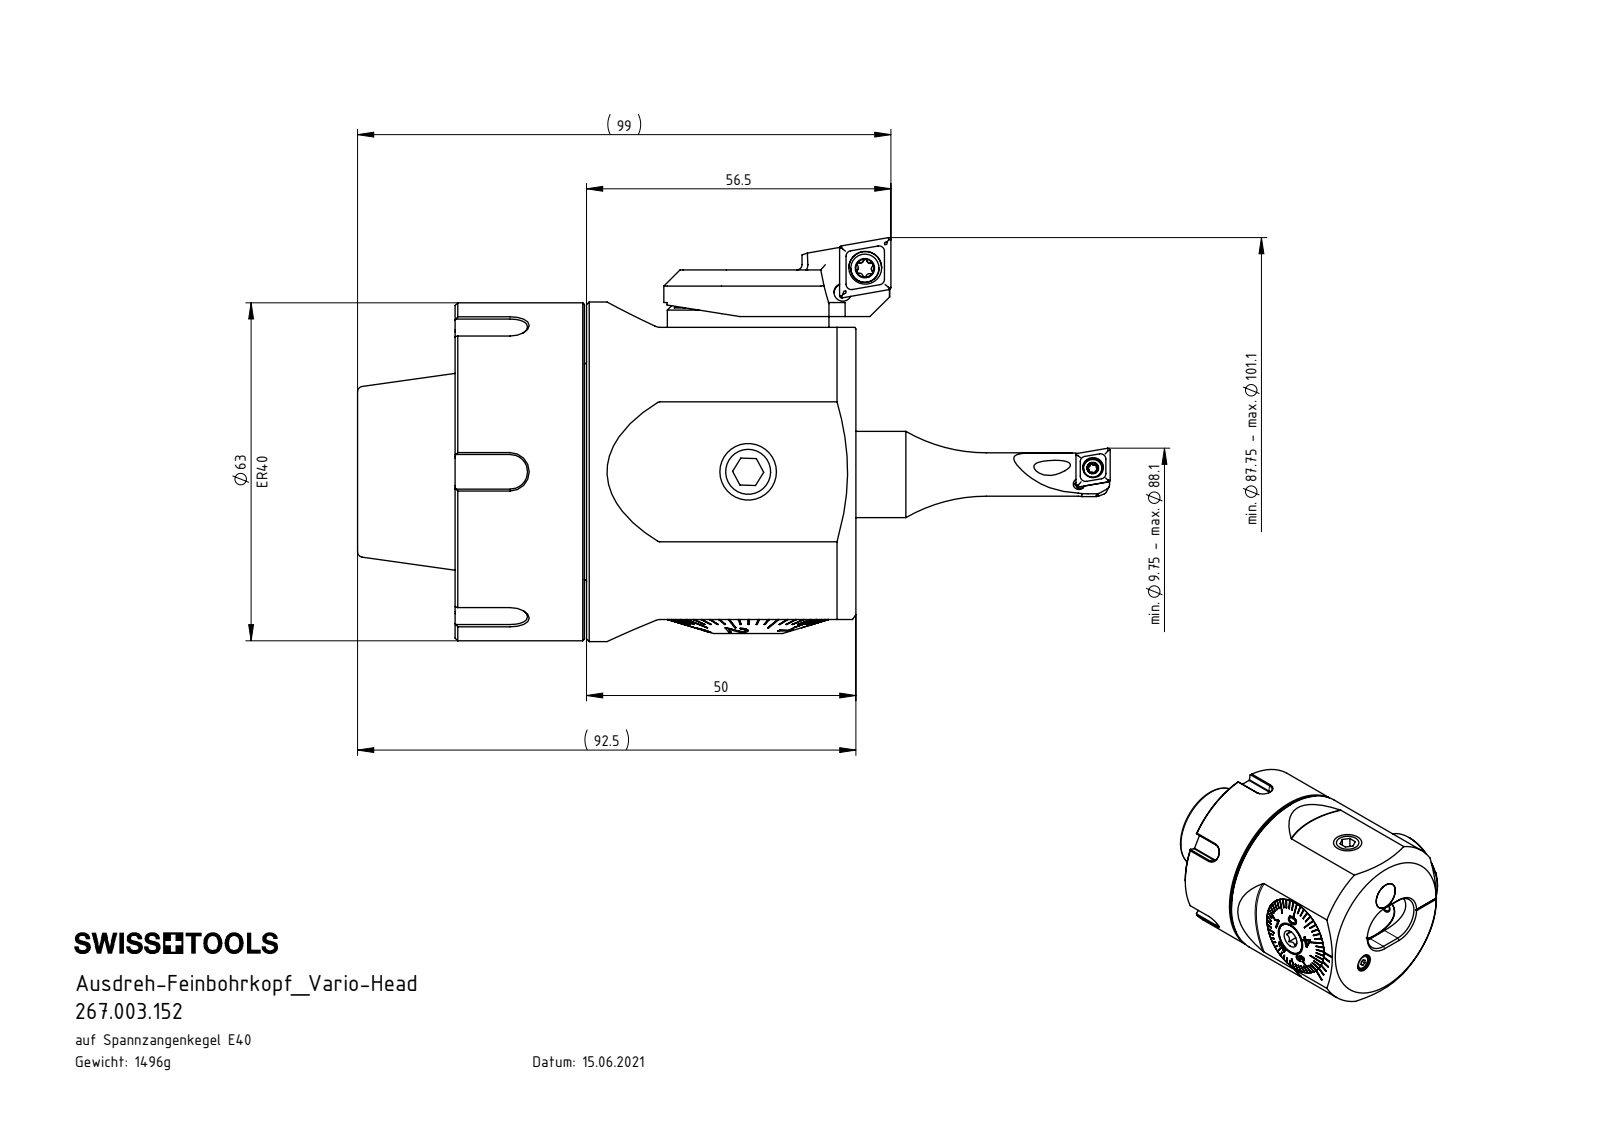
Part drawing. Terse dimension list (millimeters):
name: AV6-BG1.DA3.052_A; ISO 4026 - M5 x 16; AV6-BG1.AA4.052; AV6-BG2.014.011_B_Abgedreht (+8 more)
written by: SolidWorks 2017 (AUTOMOTIVE_DESIGN)
unit: mm
bodies: 16 solids, 676 faces (374 planar, 92 cylindrical, 210 other)
size: 92.5 × 64.76 × 63
volume: 191 350 mm³; area: 59 919 mm²
holes: 2× ⌀3.3, 2× ⌀6, 2× ⌀8.5, 1× ⌀1, 1× ⌀2.5, 1× ⌀4.2, 1× ⌀8, 1× ⌀10, 1× ⌀11.75, 1× ⌀12, 1× ⌀12.4, 1× ⌀14
bosses: 2× ⌀10, 1× ⌀63, 1× ⌀62.7, 1× ⌀40, 1× ⌀37.5, 1× ⌀30, 1× ⌀29.98, 1× ⌀29.9
rounds: 12× R0.3, 4× R0.5, 4× R1.4, 4× R1.9, 3× R3.2, 3× R8.5, 2× R1.5, 1× R1
face distances: 50, 0.4, 50.4, 24, 24.4, 74.4, 57.7, 2.7, 2.8, 2.5
hole spacings: 1.66, 10.5, 14.5, 14.59, 15.33, 16.6, 27.25
